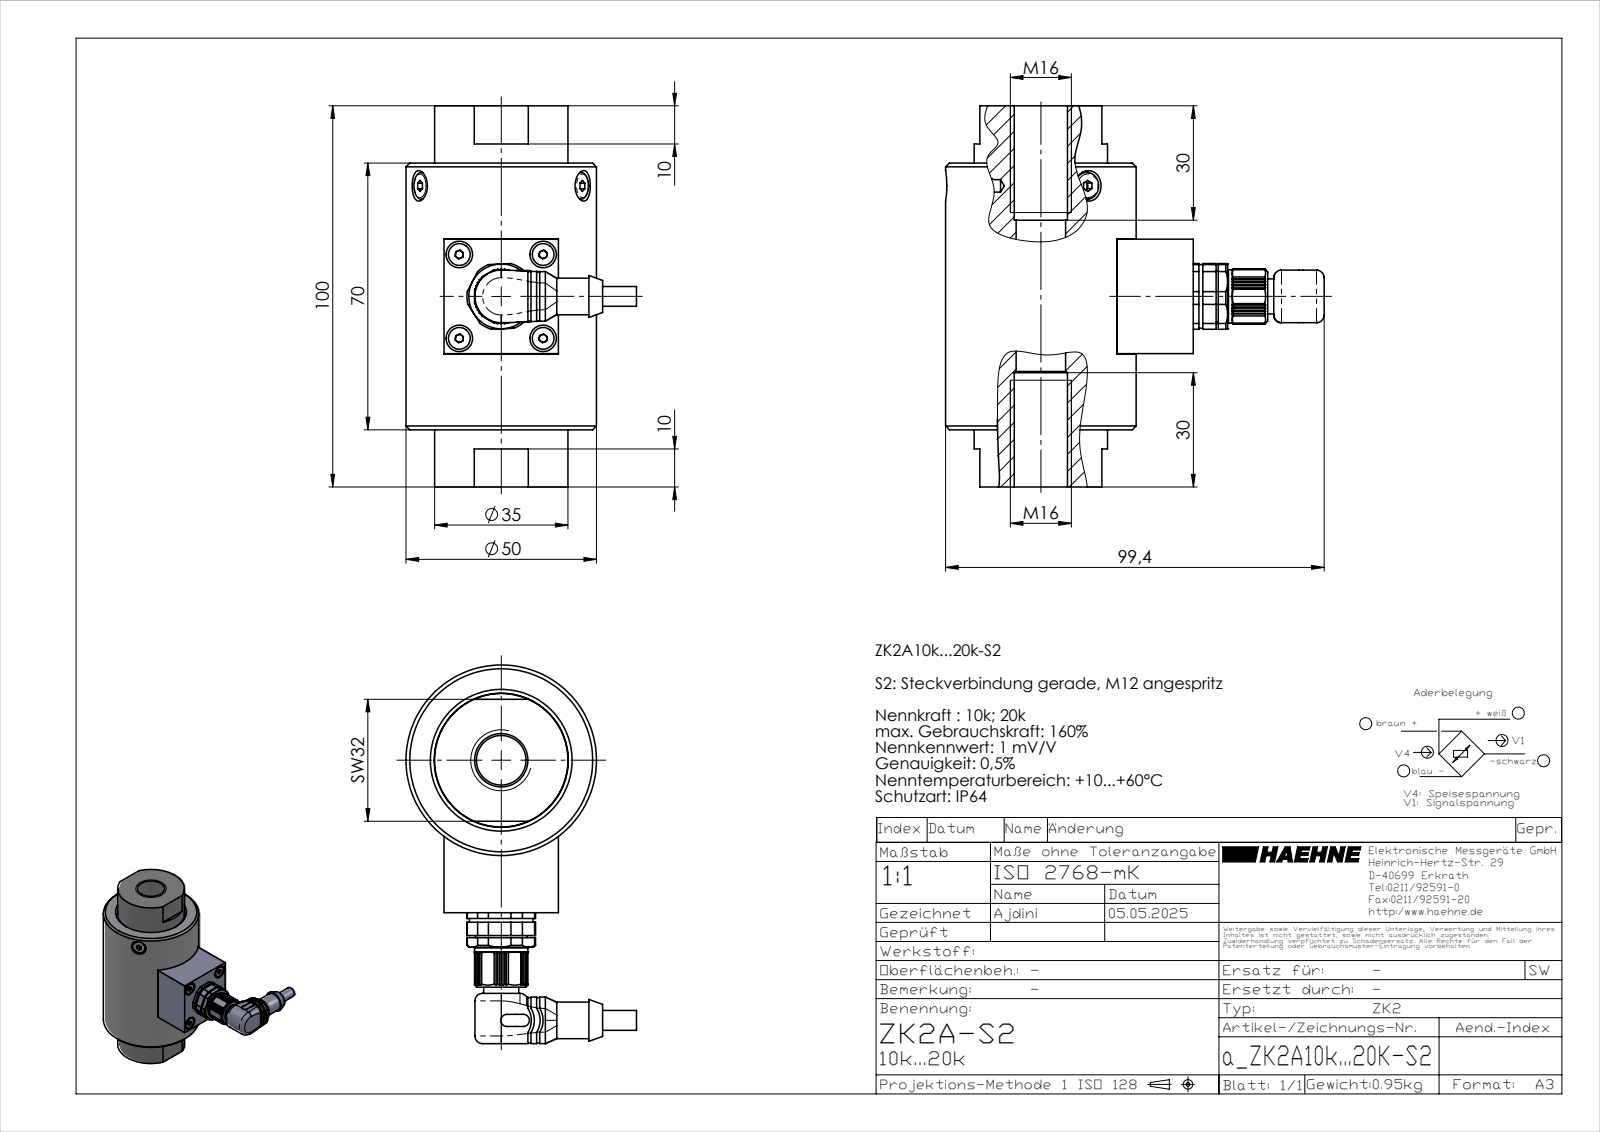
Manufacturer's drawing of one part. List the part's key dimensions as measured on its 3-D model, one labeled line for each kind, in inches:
Part name (STEP PRODUCT): a_ZK2A10k...20K-S2 STEP
STEP written by: SolidWorks 2023 (AUTOMOTIVE_DESIGN)
Units: inches
Bodies: 12 solids, 871 faces (487 planar, 207 cylindrical, 177 other)
Overall size (bounding box): 3.937 × 3.911 × 2.383
Volume: 10.05 in³ · Surface area: 79.94 in²
Round holes (diameter × count): ⌀0.043 ×4, ⌀0.045 ×4, ⌀0.063 ×4, ⌀0.073 ×4, ⌀0.098 ×4, ⌀0.134 ×4, ⌀0.13 ×3, ⌀0.169 ×3, ⌀0.315 ×3, ⌀0.047 ×1, ⌀0.33 ×1, ⌀0.331 ×1
Round bosses / shafts (diameter × count): ⌀0.224 ×4, ⌀0.118 ×4, ⌀0.071 ×4, ⌀0.061 ×4, ⌀0.059 ×4, ⌀0.039 ×4, ⌀0.276 ×3, ⌀0.157 ×3
Partial cylindrical surfaces — rounded edges, fillets, slot ends (radius × count): R0.008 ×16, R0.012 ×9, R0.016 ×4, R0.021 ×4, R0.039 ×4, R0.05 ×4, R0.236 ×4, R0.063 ×2
Main face-to-face distances: 0.787, 0.591, 3.346, 1.181, 1.378, 2.559, 1.969, 3.937, 2.756, 0.197
Hole centre spacings: 0.547, 0.685, 0.098, 0.139, 0.613, 0.866, 0.197, 0.831
